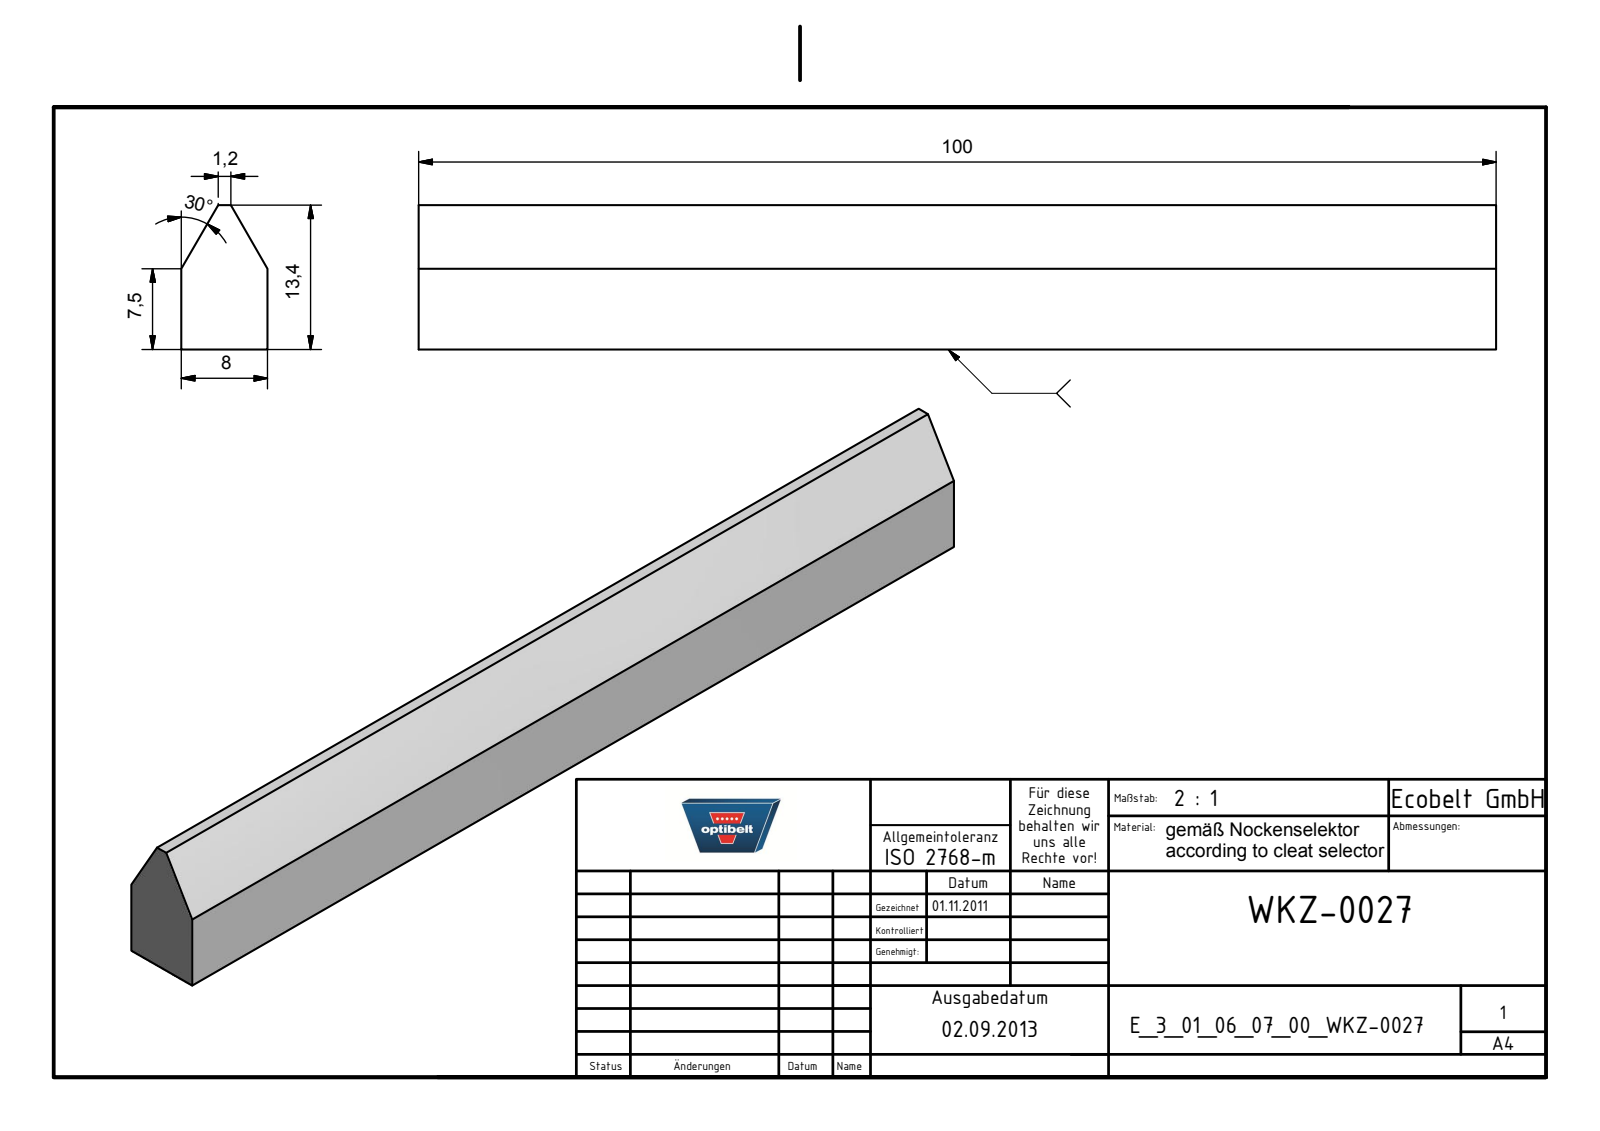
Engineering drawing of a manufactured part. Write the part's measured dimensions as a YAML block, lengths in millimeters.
part_name: "E_3_01_06_07_00_WKZ-0027"
step_written_by: "Autodesk Inventor 2021 (AUTOMOTIVE_DESIGN)"
units: millimeters
bodies: {solids: 1, faces: 8, planar: 8, cylindrical: 0, other: 0}
overall_size: [100, 13.39, 8]
volume: 8709
surface_area: 3954
face_to_face_distances: [8, 13.39, 100]
